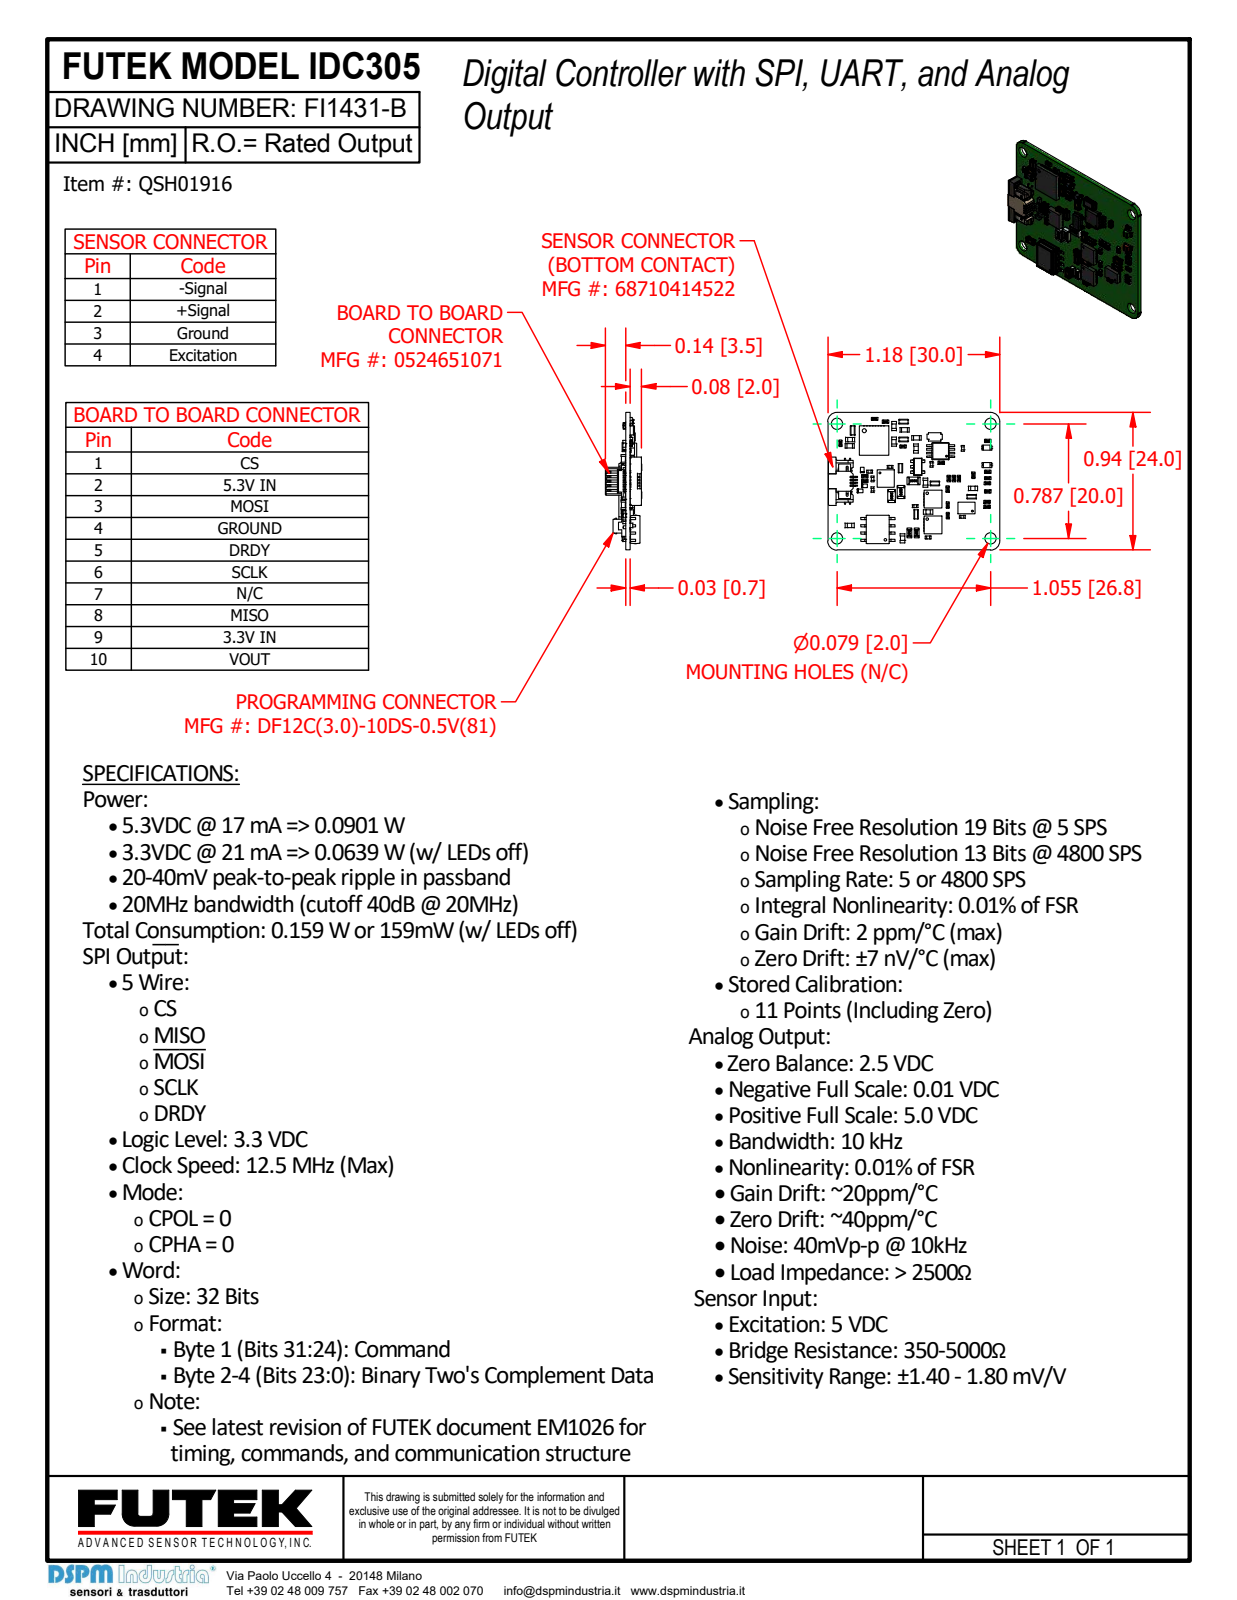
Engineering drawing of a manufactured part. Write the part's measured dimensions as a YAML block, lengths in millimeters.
part_name: "QLA405_Shrinkwrap_1"
step_written_by: "Autodesk Inventor 2018 (AUTOMOTIVE_DESIGN)"
units: millimeters
bodies: {solids: 1, faces: 146, planar: 98, cylindrical: 46, other: 2}
overall_size: [173.4, 18, 9]
volume: 1200
surface_area: 3370
round_holes:
  - {diameter: 2.2, count: 4}
  - {diameter: 3.7, count: 4}
  - {diameter: 2, count: 2}
  - {diameter: 6.3, count: 1}
  - {diameter: 7.1, count: 1}
  - {diameter: 10.1, count: 1}
round_bosses_or_shafts:
  - {diameter: 18, count: 1}
partial_cylinders:
  - {radius: 0.9, count: 8}
  - {radius: 0.2, count: 2}
  - {radius: 0.3, count: 2}
  - {radius: 0.5, count: 2}
face_to_face_distances: [2.4, 0.3, 2.7, 0.4, 6.6, 6.3, 9, 6.2, 6.5, 8.9]
hole_center_spacings: [6.5, 3.6, 13.3, 7.2, 11.3, 13, 14.5]
